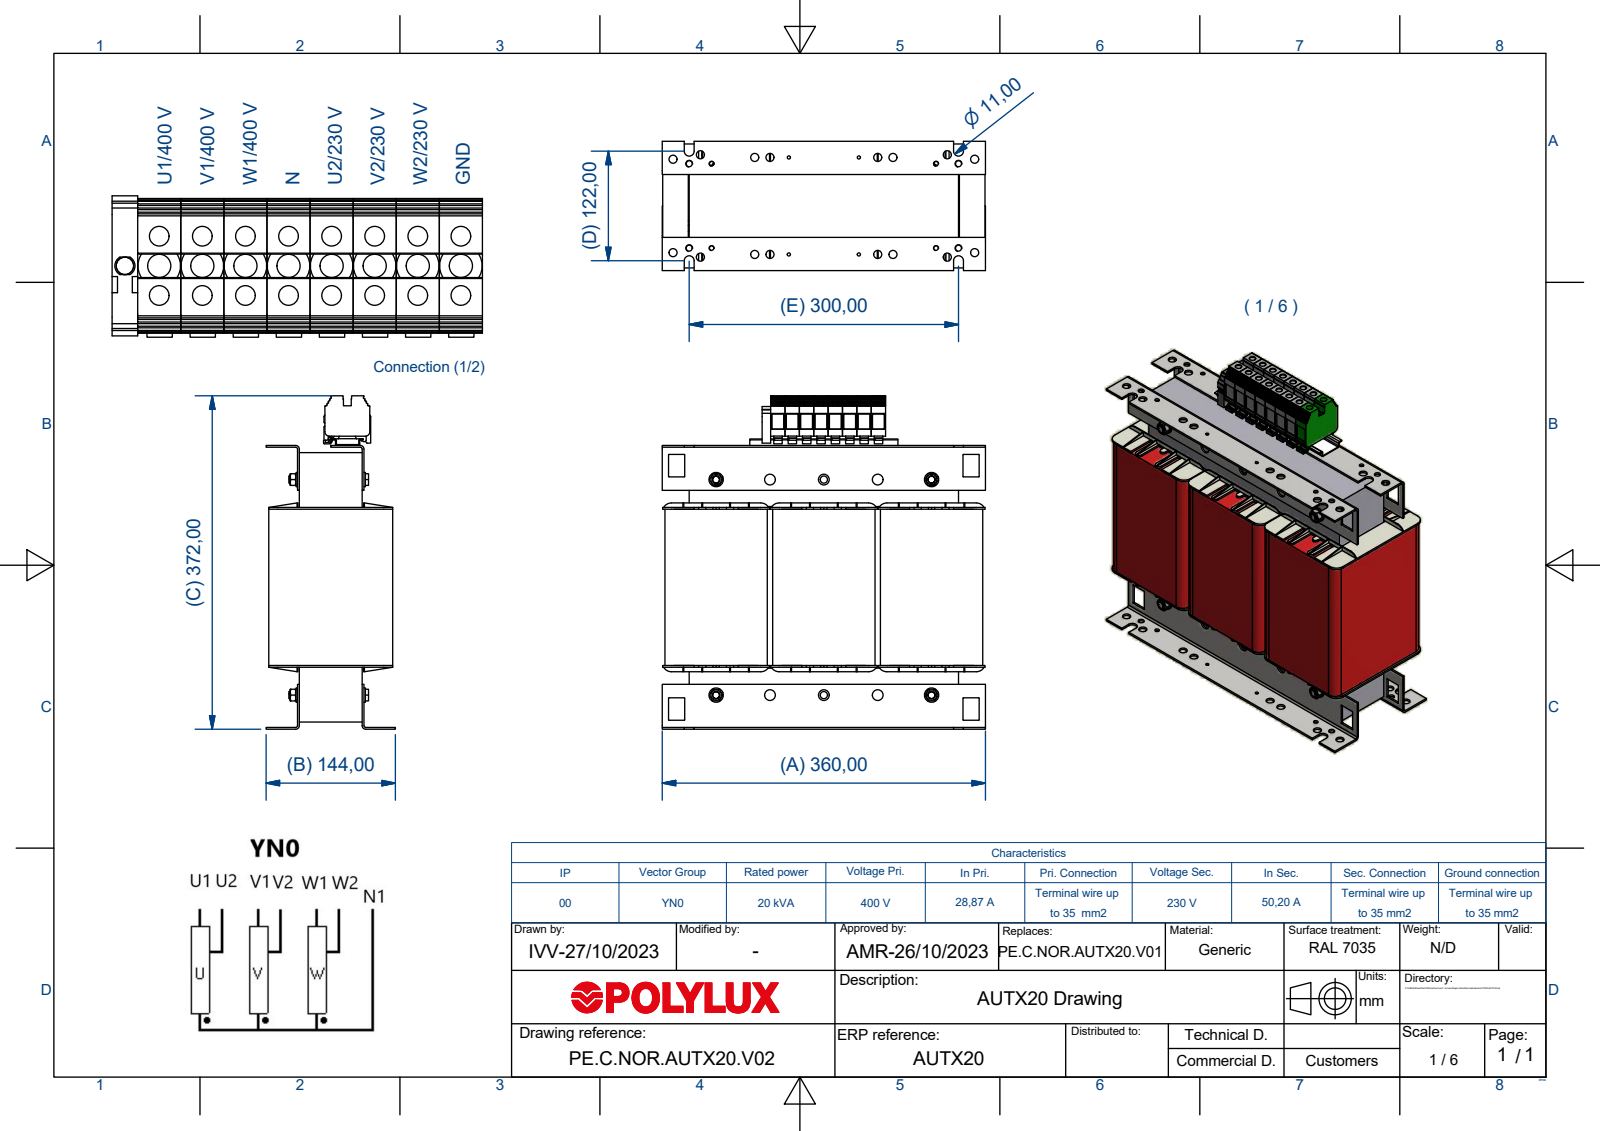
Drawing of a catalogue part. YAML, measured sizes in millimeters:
part_name: "AUTX20"
step_written_by: "Autodesk Inventor 2018 (AUTOMOTIVE_DESIGN)"
units: millimeters
bodies: {solids: 0, faces: 2197, planar: 1640, cylindrical: 525, other: 32}
overall_size: [371.3, 360, 144]
round_holes:
  - {diameter: 9, count: 20}
  - {diameter: 7.3, count: 16}
  - {diameter: 4.92, count: 6}
  - {diameter: 6.65, count: 6}
  - {diameter: 12, count: 6}
  - {diameter: 3.5, count: 4}
  - {diameter: 8, count: 2}
  - {diameter: 8.6, count: 2}
round_bosses_or_shafts:
  - {diameter: 16, count: 4}
  - {diameter: 8, count: 4}
partial_cylinders:
  - {radius: 0.5, count: 36}
  - {radius: 10, count: 36}
  - {radius: 4, count: 28}
  - {radius: 1, count: 15}
  - {radius: 5.5, count: 6}
  - {radius: 2, count: 5}
  - {radius: 0.2, count: 4}
  - {radius: 1.6, count: 4}
face_to_face_distances: [2, 1, 73, 34, 104, 70, 71, 69, 245, 6]
hole_center_spacings: [16.01, 104.75, 108, 275, 17, 18.68, 21, 25]
